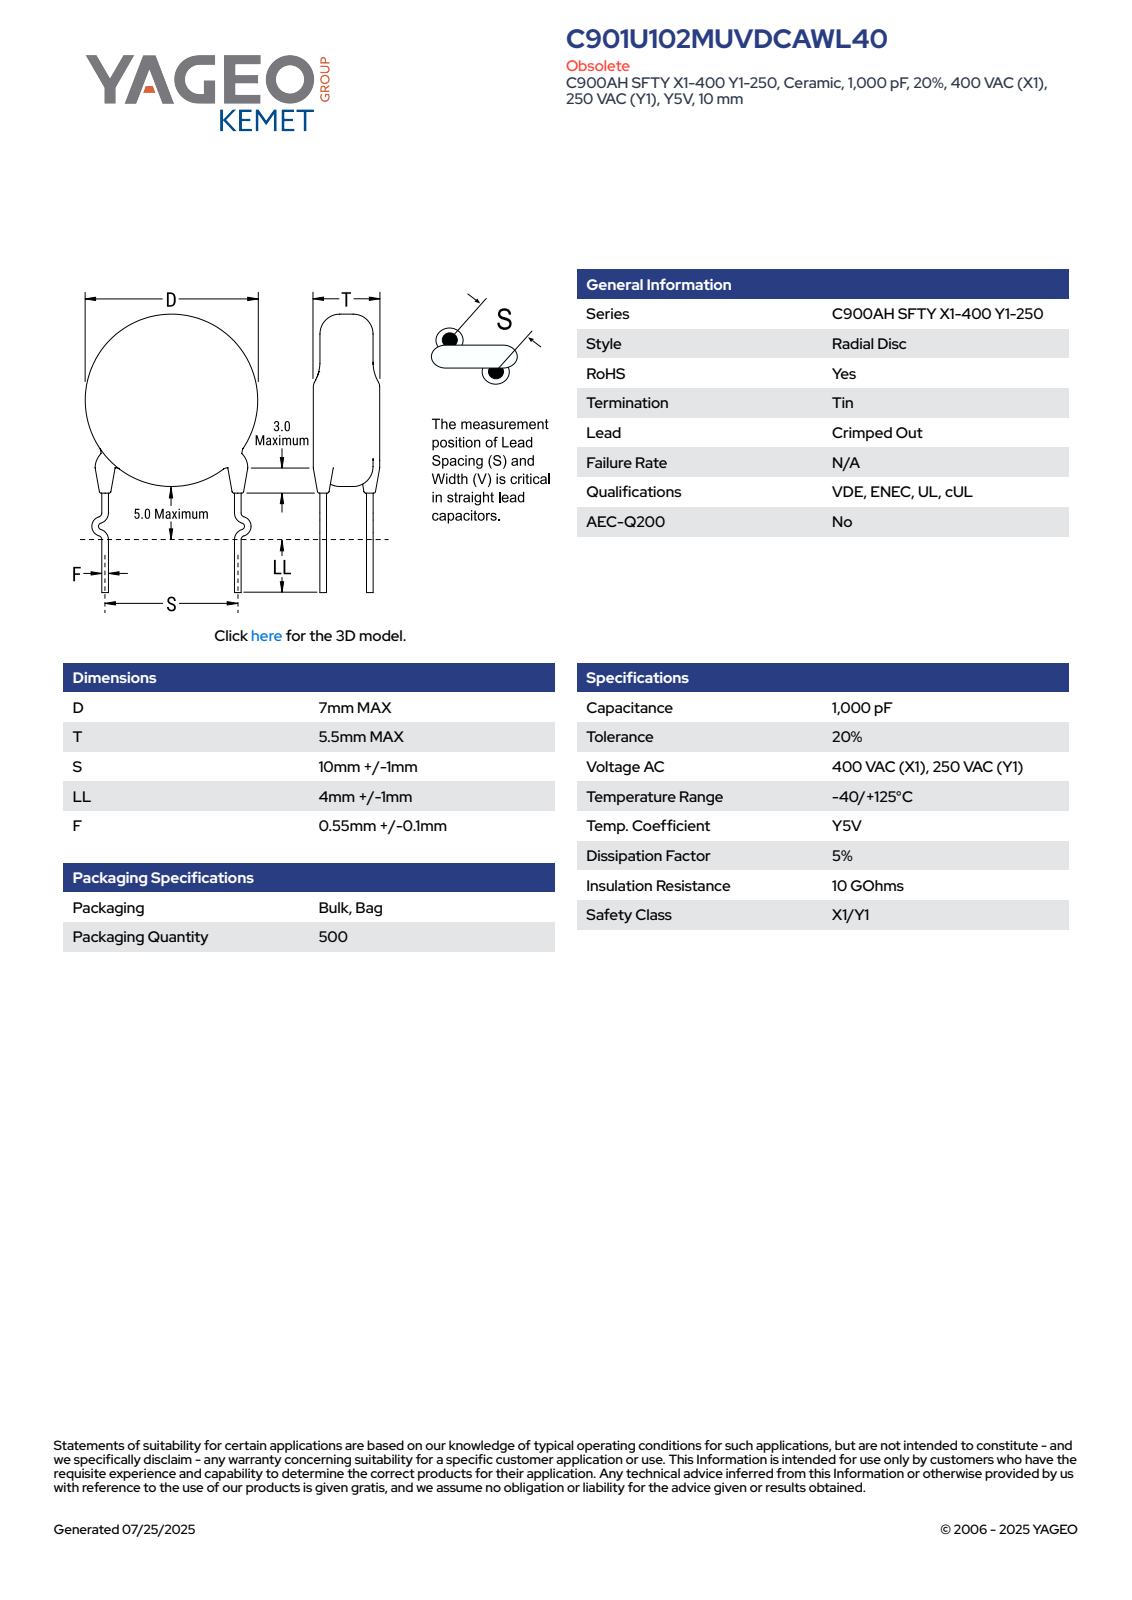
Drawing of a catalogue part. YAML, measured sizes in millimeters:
part_name: "CCD_KCOC900_D7T5.5S10LL5F0.55"
step_written_by: "SolidWorks 2014 (AUTOMOTIVE_DESIGN)"
units: millimeters
bodies: {solids: 4, faces: 93, planar: 63, cylindrical: 10, other: 20}
overall_size: [17, 13.59, 7.28]
volume: 218
surface_area: 255
round_bosses_or_shafts:
  - {diameter: 1.2, count: 4}
  - {diameter: 7, count: 1}
face_to_face_distances: [5.5, 0.73, 3.87, 3.14, 0.59, 0.32, 2.97, 1.5, 2.16, 2.24]
